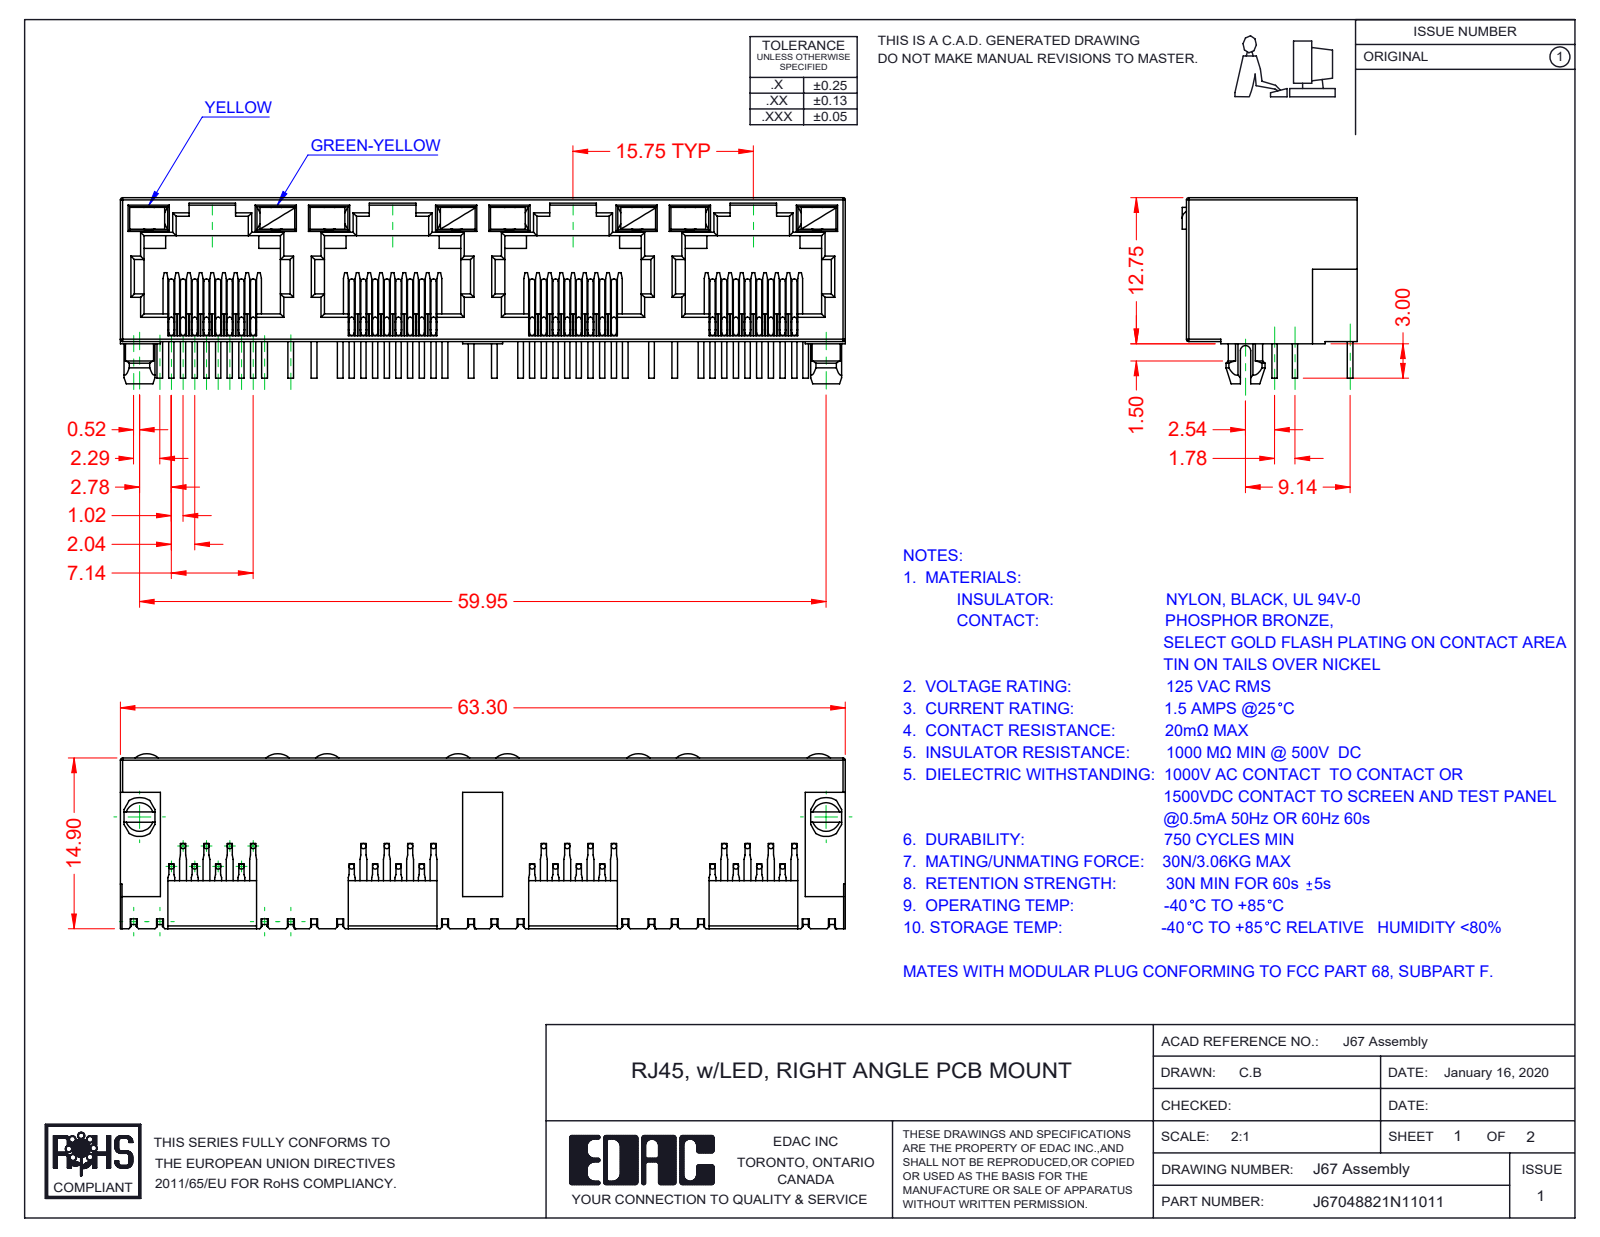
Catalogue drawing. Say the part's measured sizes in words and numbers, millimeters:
The part is named "67 Contacts; J67048822N15011; 67 LED RH_5-Green-Yellow; 67 Insulator (+1 more)". Its 3-D file was written by "SolidWorks 2016 (CONFIG_CONTROL_DESIGN)". It is 41 solids with 2473 faces: 1781 planar, 484 cylindrical and 208 other. Overall it measures 63.3 by 16.25 by 15.28 millimeters. Its volume is 5 159 cubic millimeters and its surface area 11 573 square millimeters. Round bosses or shafts: 96 of diameter 0.46. Partial cylindrical surfaces (rounded edges, fillets, slot ends): 66 of radius 0.2, 29 of radius 0.3, 9 of radius 0.45, 8 of radius 1.55, 2 of radius 1.5, 2 of radius 1.7, 1 of radius 0.35, 1 of radius 1. The main face-to-face distances are 0.5, 12.55, 1.89, 0.89, 10, 15.75, 1, 1.39, 11, 11.89.
